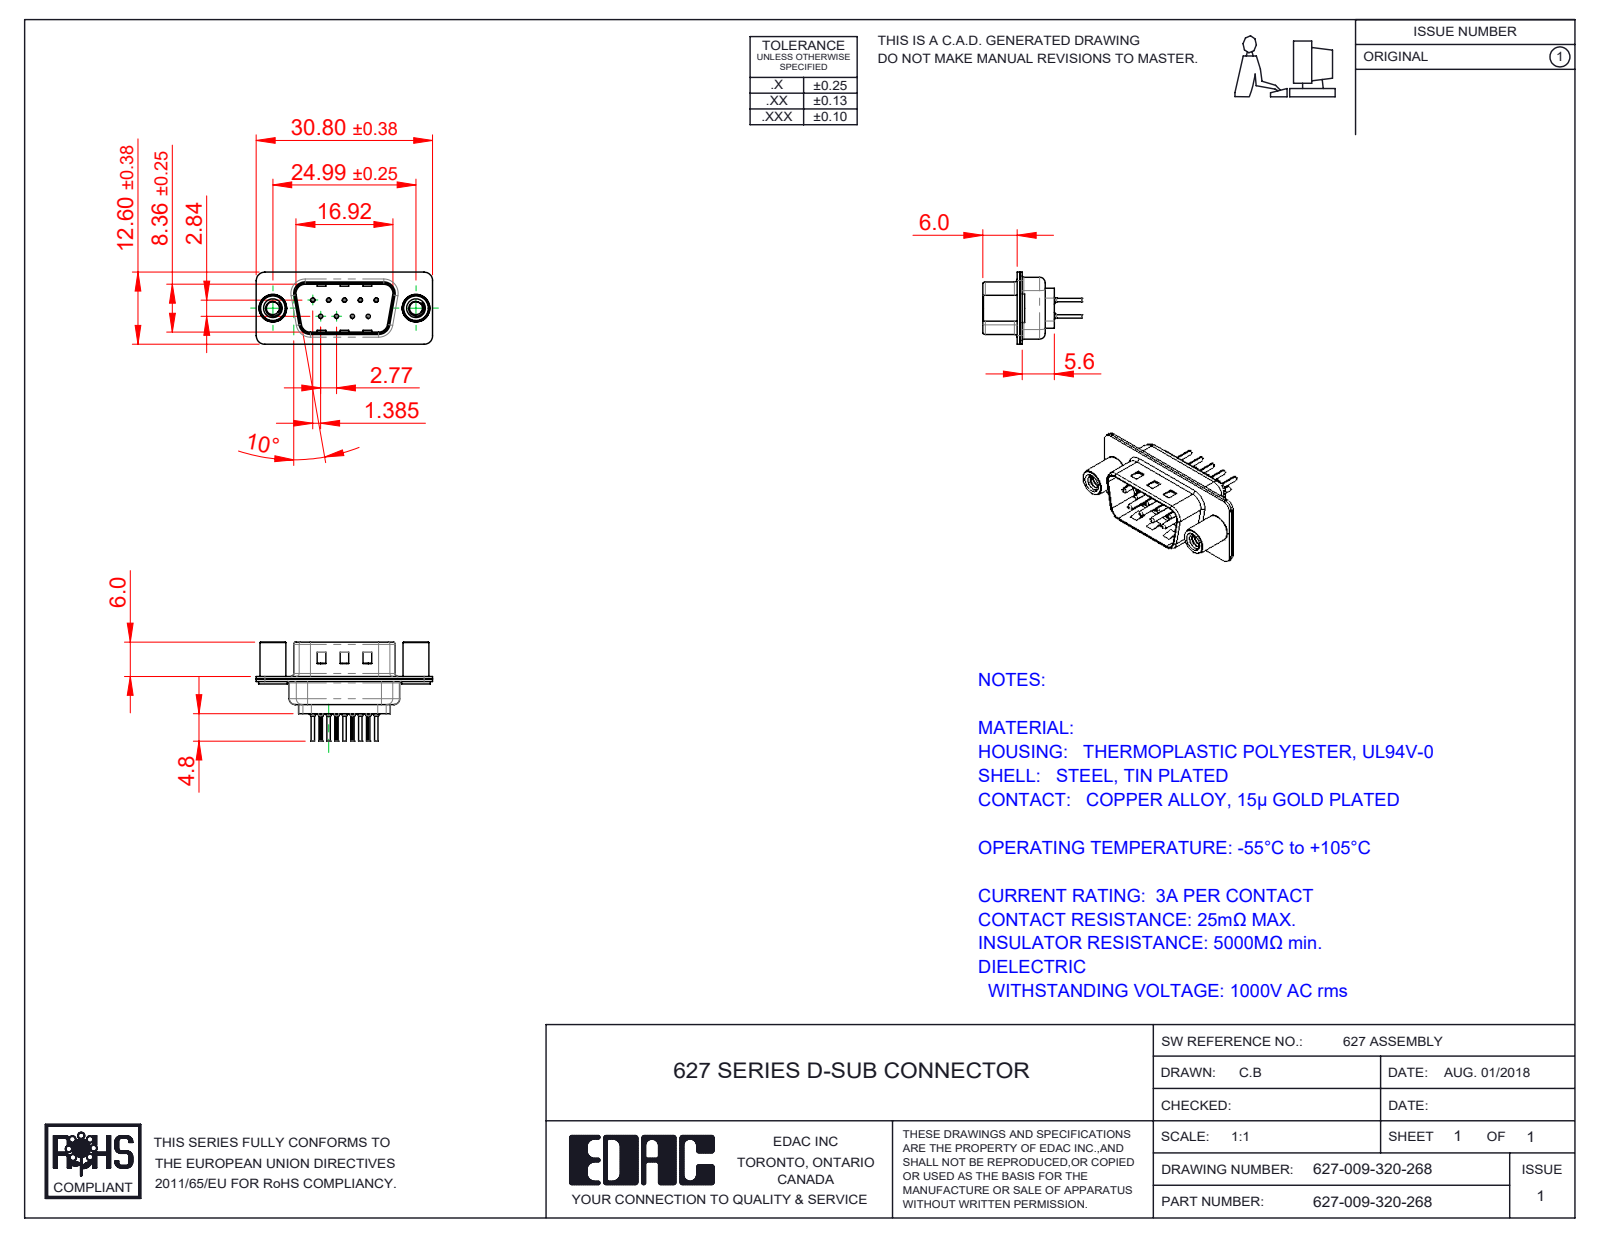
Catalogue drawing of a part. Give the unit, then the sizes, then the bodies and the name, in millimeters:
Units: millimetres
Overall size (bounding box): 30.8 × 17.3 × 12.6
Round holes (diameter × count): ⌀0.2 ×9, ⌀0.35 ×9, ⌀1.1 ×9, ⌀1.6 ×9, ⌀2.26 ×2, ⌀4 ×2, ⌀4.8 ×2
Round bosses / shafts (diameter × count): ⌀2 ×9, ⌀1.5 ×9, ⌀0.75 ×9, ⌀0.6 ×9, ⌀5 ×2, ⌀4.9 ×2, ⌀4.5 ×2
Partial cylindrical surfaces — rounded edges, fillets, slot ends (radius × count): R0.1 ×18, R1.5 ×18, R2 ×12, R0.5 ×8, R1.6 ×8, R0.25 ×4, R0.6 ×4, R0.65 ×4
Main face-to-face distances: 0.4, 0.45, 0.9, 0.82, 9.58, 1.4, 8.76, 0.5, 1.5, 5.6
Hole centre spacings: 3.16, 2.77, 5.54, 5.03, 5.04, 8.31, 7.48, 7.49
Volume: 1 375 mm³ · Surface area: 4 129 mm²
Bodies: 14 solids, 1220 faces (325 planar, 490 cylindrical, 405 other)
Part name (STEP PRODUCT): 627 4-40 Threaded Standoff; 627 Housing_09 LP; 627-009-320-068; 627 Shell Front_09 Contacts (+3 more)
STEP written by: SolidWorks 2020 (CONFIG_CONTROL_DESIGN)
